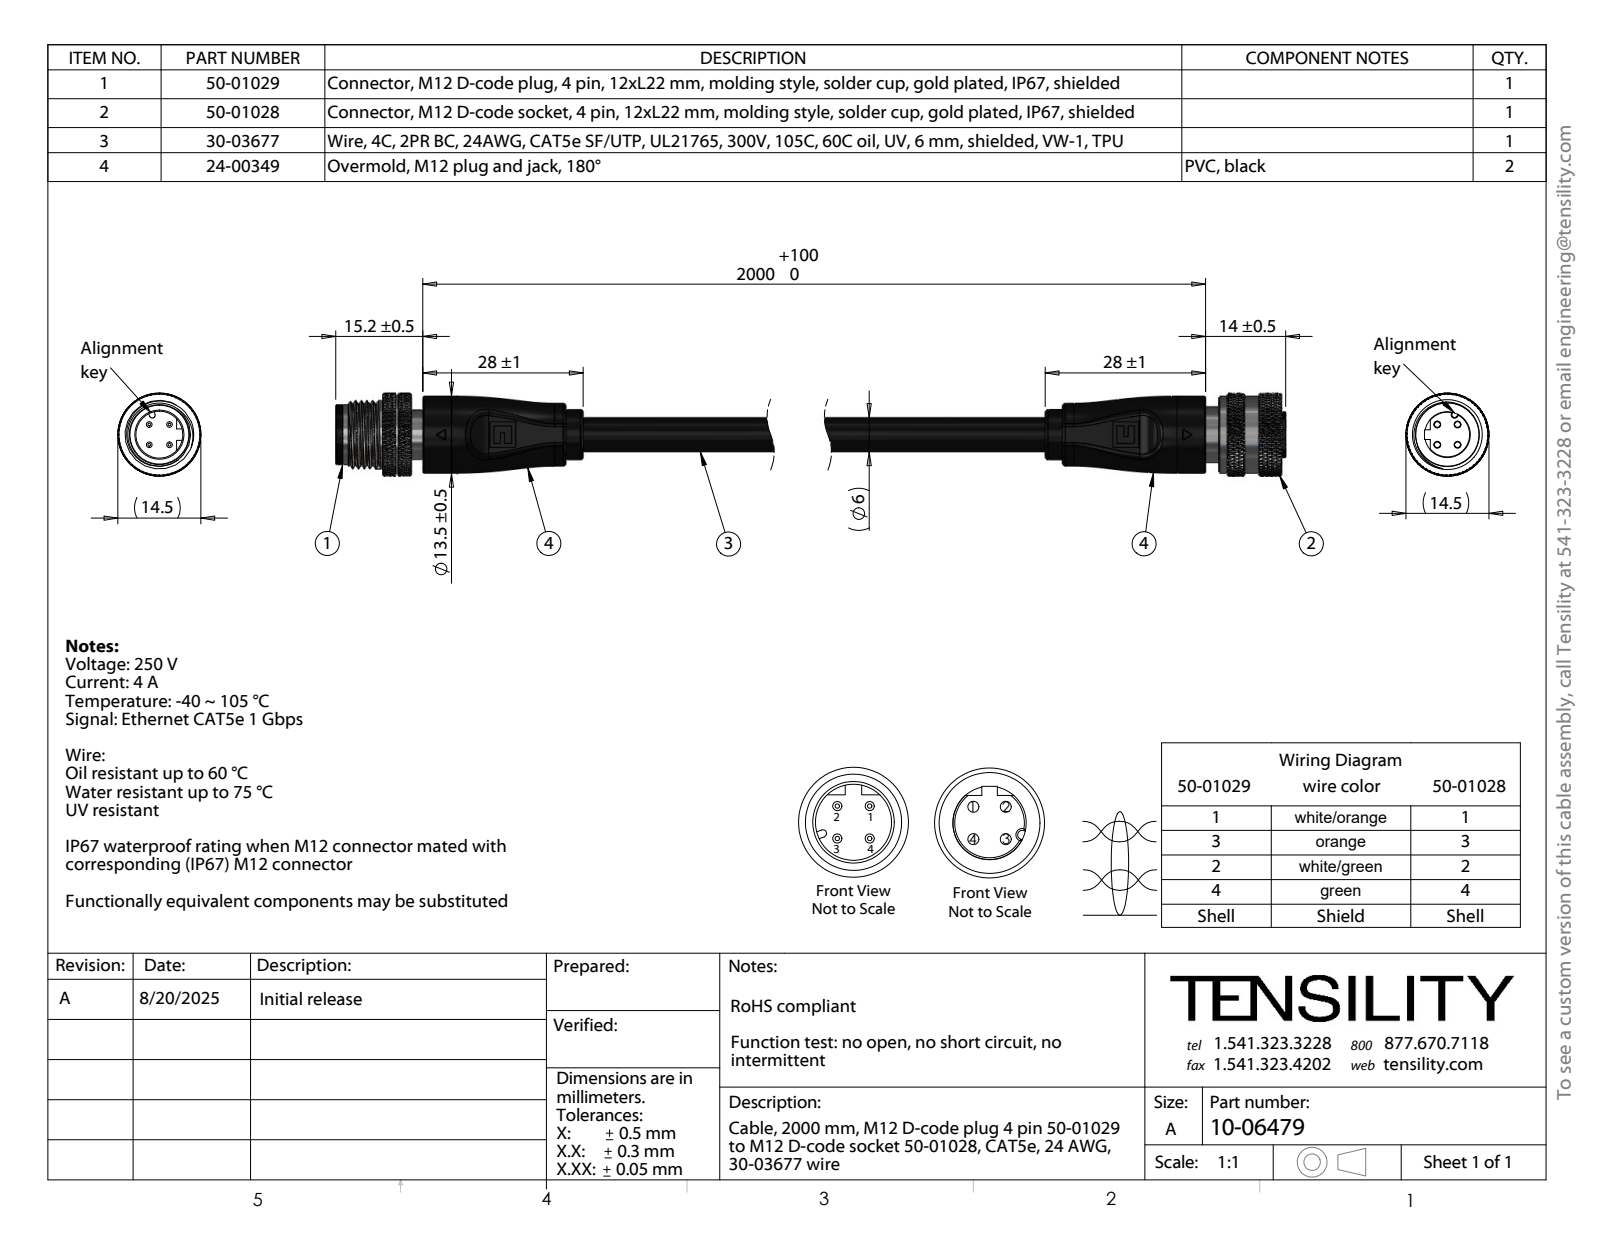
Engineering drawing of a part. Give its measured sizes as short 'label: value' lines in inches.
name: 50-01028-02_默认; 50-01028-04_默认; 30-03677_blunt cut; 50-01029-04_默认 (+8 more)
written by: SolidWorks 2025 (CONFIG_CONTROL_DESIGN)
unit: in
bodies: 53 solids, 5792 faces (362 planar, 1477 cylindrical, 3953 other)
size: 9.26 × 0.571 × 0.571
volume: 0.838 in³; area: 47.49 in²
holes: 28× ⌀0.008, 4× ⌀0.039, 4× ⌀0.041, 4× ⌀0.043, 4× ⌀0.047, 1× ⌀0.124, 1× ⌀0.126, 1× ⌀0.14, 1× ⌀0.323, 1× ⌀0.374, 1× ⌀0.394, 1× ⌀0.441
bosses: 4× ⌀0.063, 4× ⌀0.059, 4× ⌀0.055, 1× ⌀0.571, 1× ⌀0.547, 1× ⌀0.531, 1× ⌀0.472, 1× ⌀0.433
rounds: 10× R0.004, 6× R0.016, 4× R0.02, 2× R0.059, 2× R0.077, 2× R0.197, 1× R0.22, 1× R0.266
face distances: 8.11, 0.276, 1.102, 7.008, 0.079, 8.189, 0.15, 8.339, 8.201, 0.228
hole spacings: 0.075, 0.014, 0.082, 0.042, 0.035, 0.043, 0.049, 0.071
